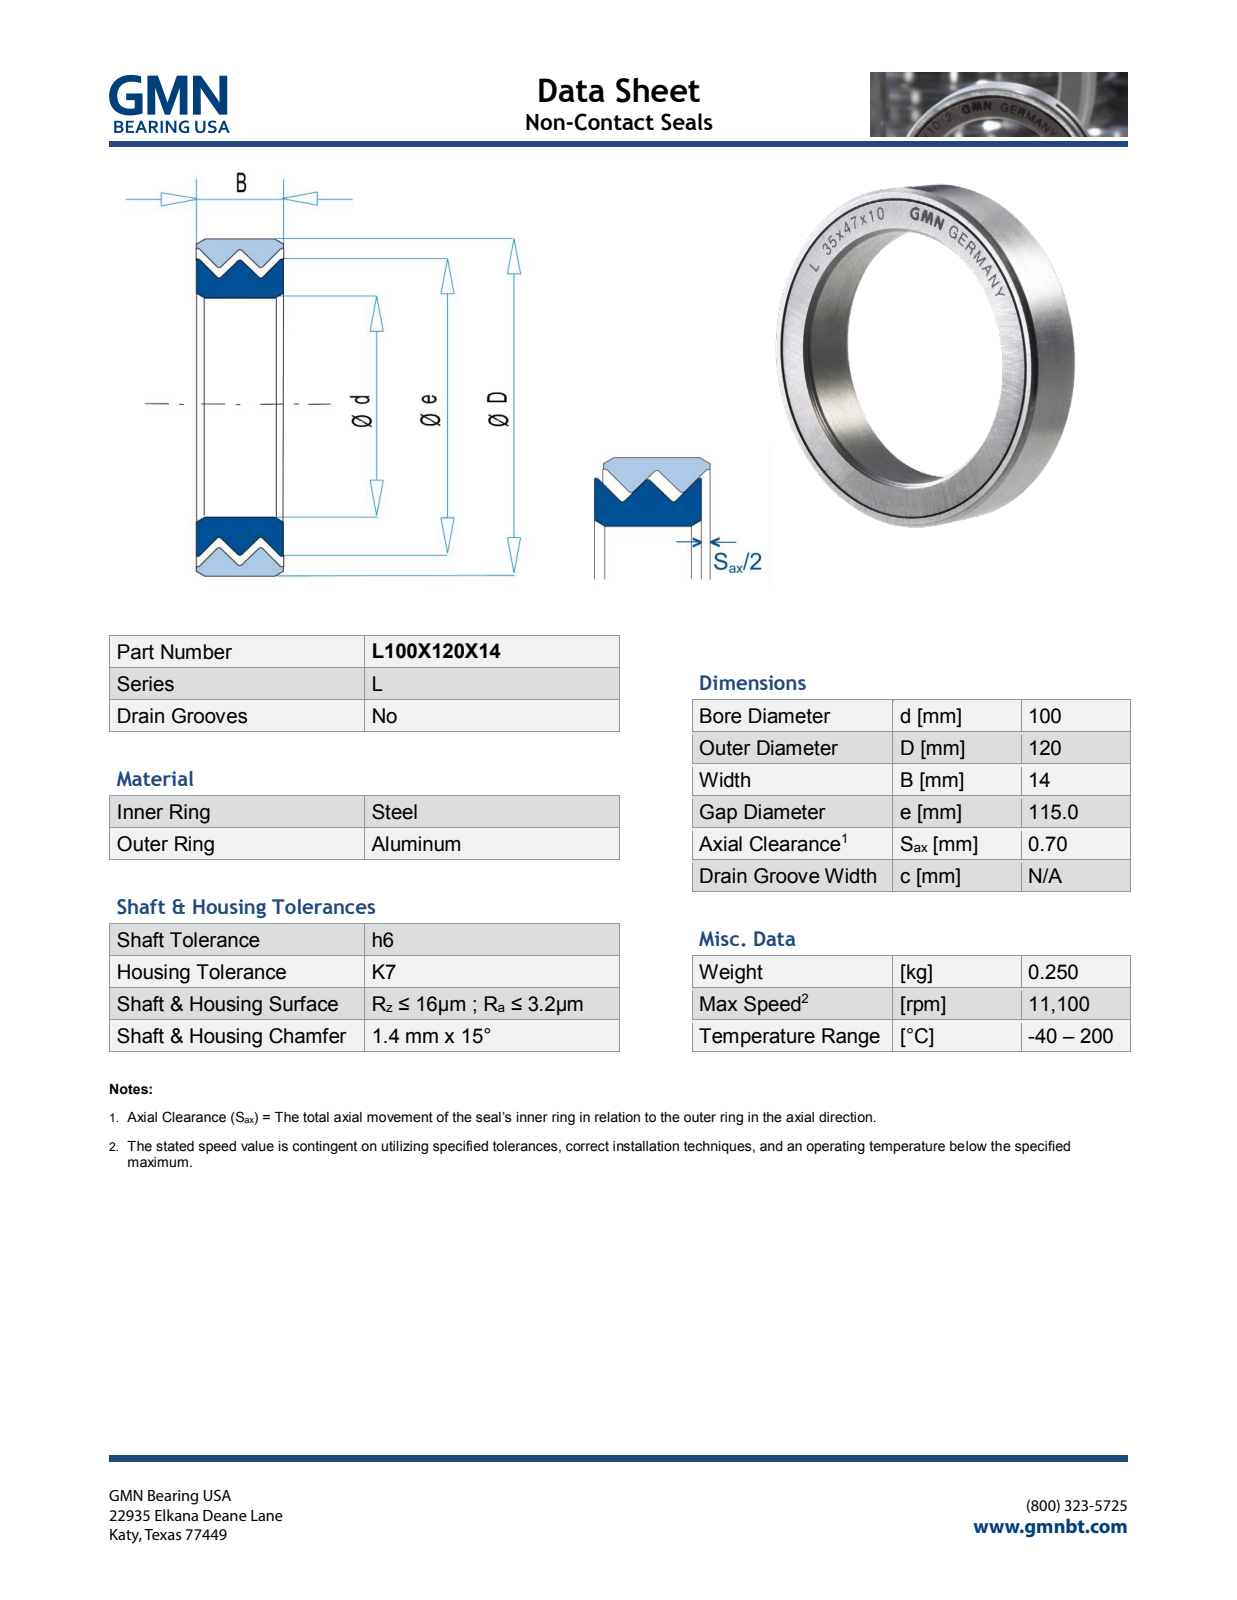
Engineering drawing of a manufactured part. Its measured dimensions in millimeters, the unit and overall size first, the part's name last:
Units: millimetres
Overall size (bounding box): 120 × 120 × 14.07
Round holes (diameter × count): ⌀100 ×1, ⌀115.49 ×1
Round bosses / shafts (diameter × count): ⌀120 ×1, ⌀115 ×1
Main face-to-face distances: 14, 14.07, 0.62, 4.92, 0.61, 0.63, 4.31, 4.1, 3.69, 4.3
Volume: 46 510 mm³ · Surface area: 27 846 mm²
Bodies: 2 solids, 574 faces (518 planar, 12 cylindrical, 44 other)
Part name (STEP PRODUCT): L100X120X14_PRT
STEP written by: PRO/ENGINEER BY PARAMETRIC TECHNOLOGY CORPORATION, 2013150 (AUTOMOTIVE_DESIGN)
